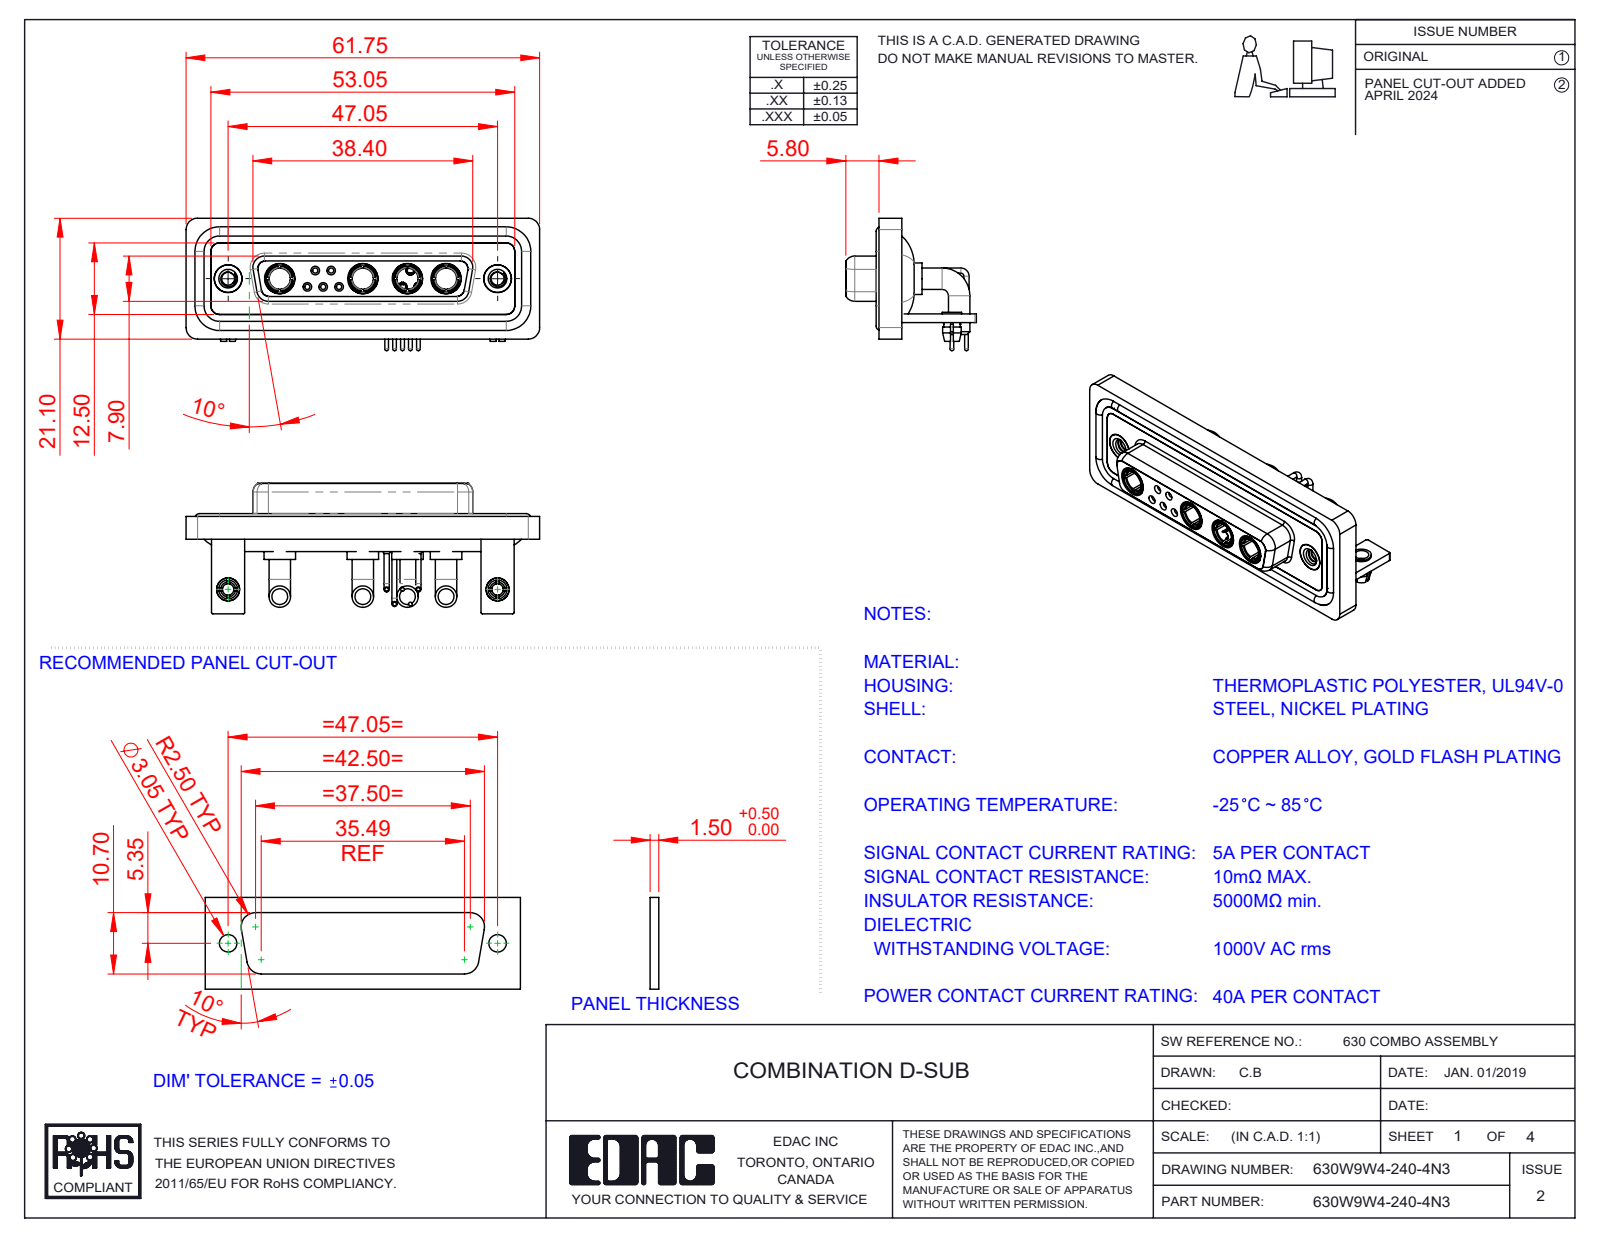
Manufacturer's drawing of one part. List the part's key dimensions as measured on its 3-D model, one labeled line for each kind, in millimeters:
Part name (STEP PRODUCT): 630Combo Shell Rear_25 Contacts; 630Combo Waterproof Housing_25 Contacts; 630Combo Shell Front_25 Contacts; 630Combo Contact Row 2_50 Contacts (+7 more)
STEP written by: SolidWorks 2023 (CONFIG_CONTROL_DESIGN)
Units: millimetres
Bodies: 24 solids, 1103 faces (364 planar, 459 cylindrical, 280 other)
Overall size (bounding box): 61.75 × 23.12 × 22.8
Volume: 9 145 mm³ · Surface area: 15 168 mm²
Round holes (diameter × count): ⌀2 ×7, ⌀4.85 ×6, ⌀0.9 ×5, ⌀1.1 ×5, ⌀1.5 ×5, ⌀3.7 ×4, ⌀5.3 ×4, ⌀1.6 ×3, ⌀1.7 ×2, ⌀2.26 ×2, ⌀2.5 ×2, ⌀3.2 ×2
Round bosses / shafts (diameter × count): ⌀0.9 ×10, ⌀1.6 ×9, ⌀3.75 ×8, ⌀2 ×5, ⌀1.5 ×5, ⌀0.65 ×5, ⌀5.5 ×4, ⌀5.2 ×4
Partial cylindrical surfaces — rounded edges, fillets, slot ends (radius × count): R2 ×19, R1.5 ×18, R0.25 ×16, R1.35 ×8, R1.6 ×8, R0.5 ×5, R0.6 ×4, R0.65 ×4
Main face-to-face distances: 0.4, 1.8, 2.9, 3.7, 1.5, 4.1, 1.1, 1.4, 1.6, 2.5
Hole centre spacings: 3.16, 2.77, 5.04, 13.85, 11.08, 12.79, 15.5, 5.54
